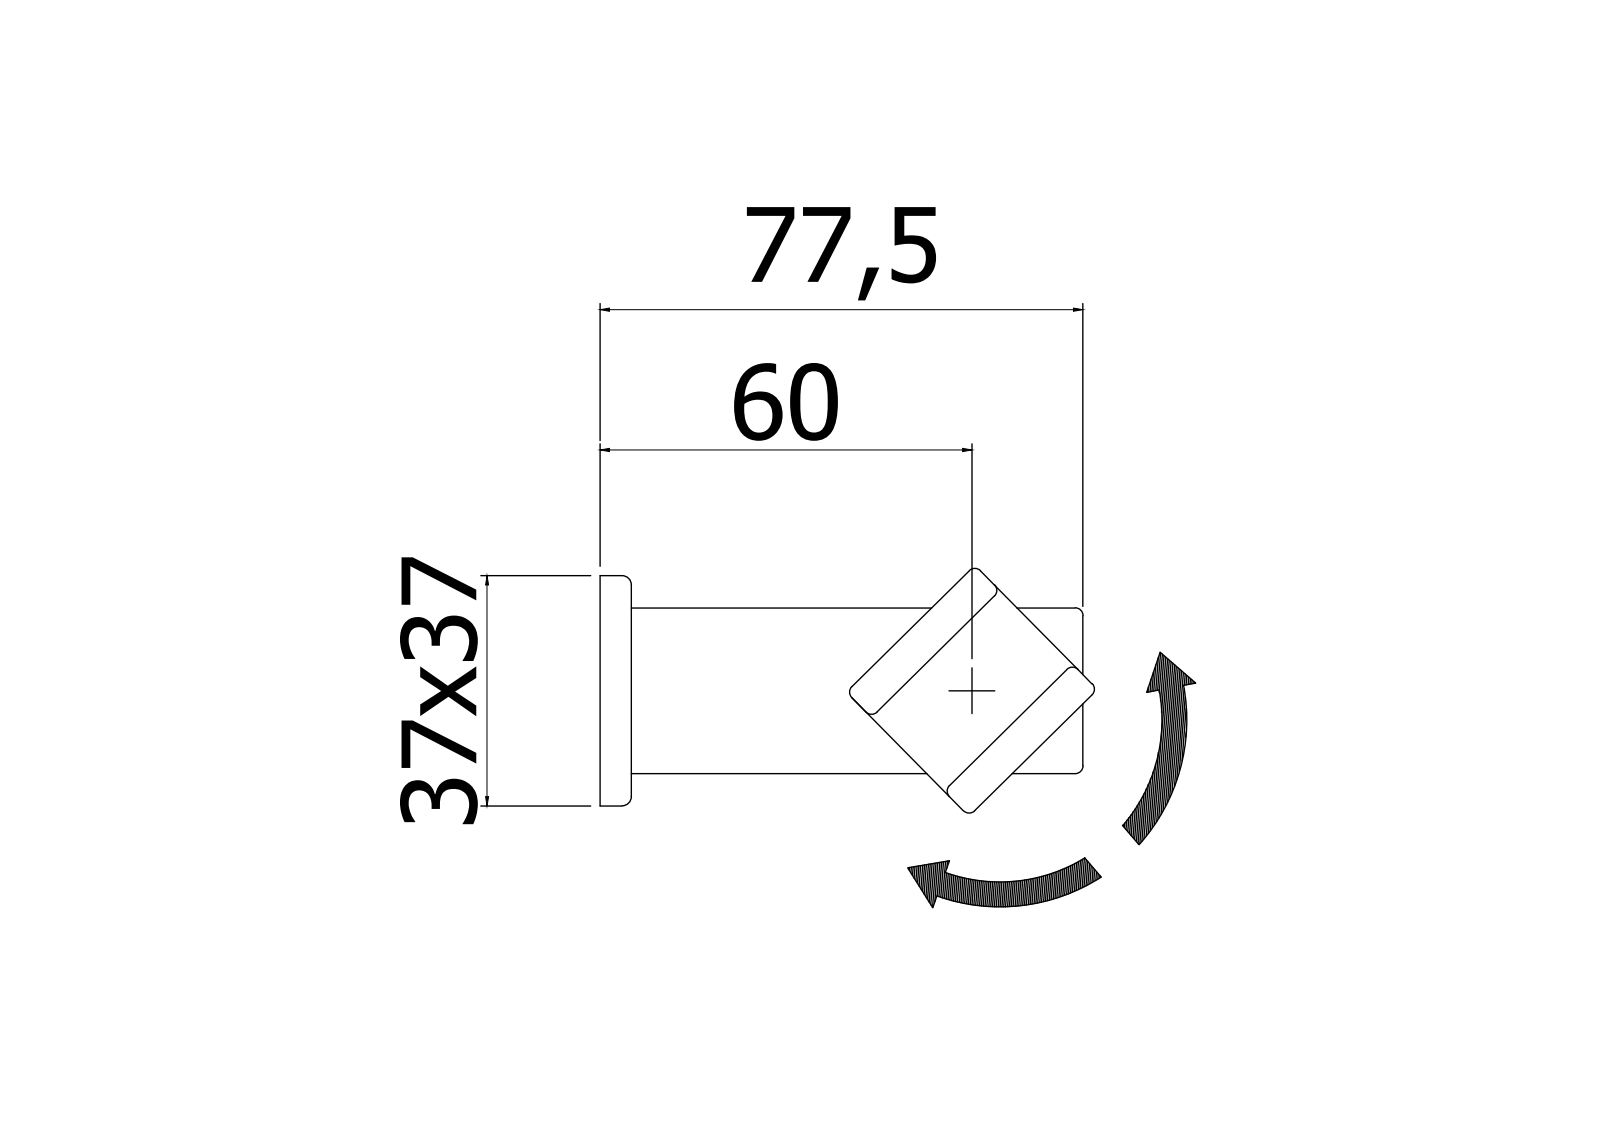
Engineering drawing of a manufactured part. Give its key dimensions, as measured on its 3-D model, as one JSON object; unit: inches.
{"part_name": "ZSUP025CR", "step_written_by": "CREO PARAMETRIC BY PTC INC, 2020044 (CONFIG_CONTROL_DESIGN)", "units": "inches", "bodies": {"solids": 0, "faces": 93, "planar": 24, "cylindrical": 40, "other": 29}, "overall_size": [3.297, 3.031, 1.457], "partial_cylinders_radius": [[0.039, 32], [0.02, 6]], "face_to_face_distances": [1.083, 0.197, 0.728, 0.177, 0.906, 3.031, 0.187, 1.27, 0.02, 0.925]}
